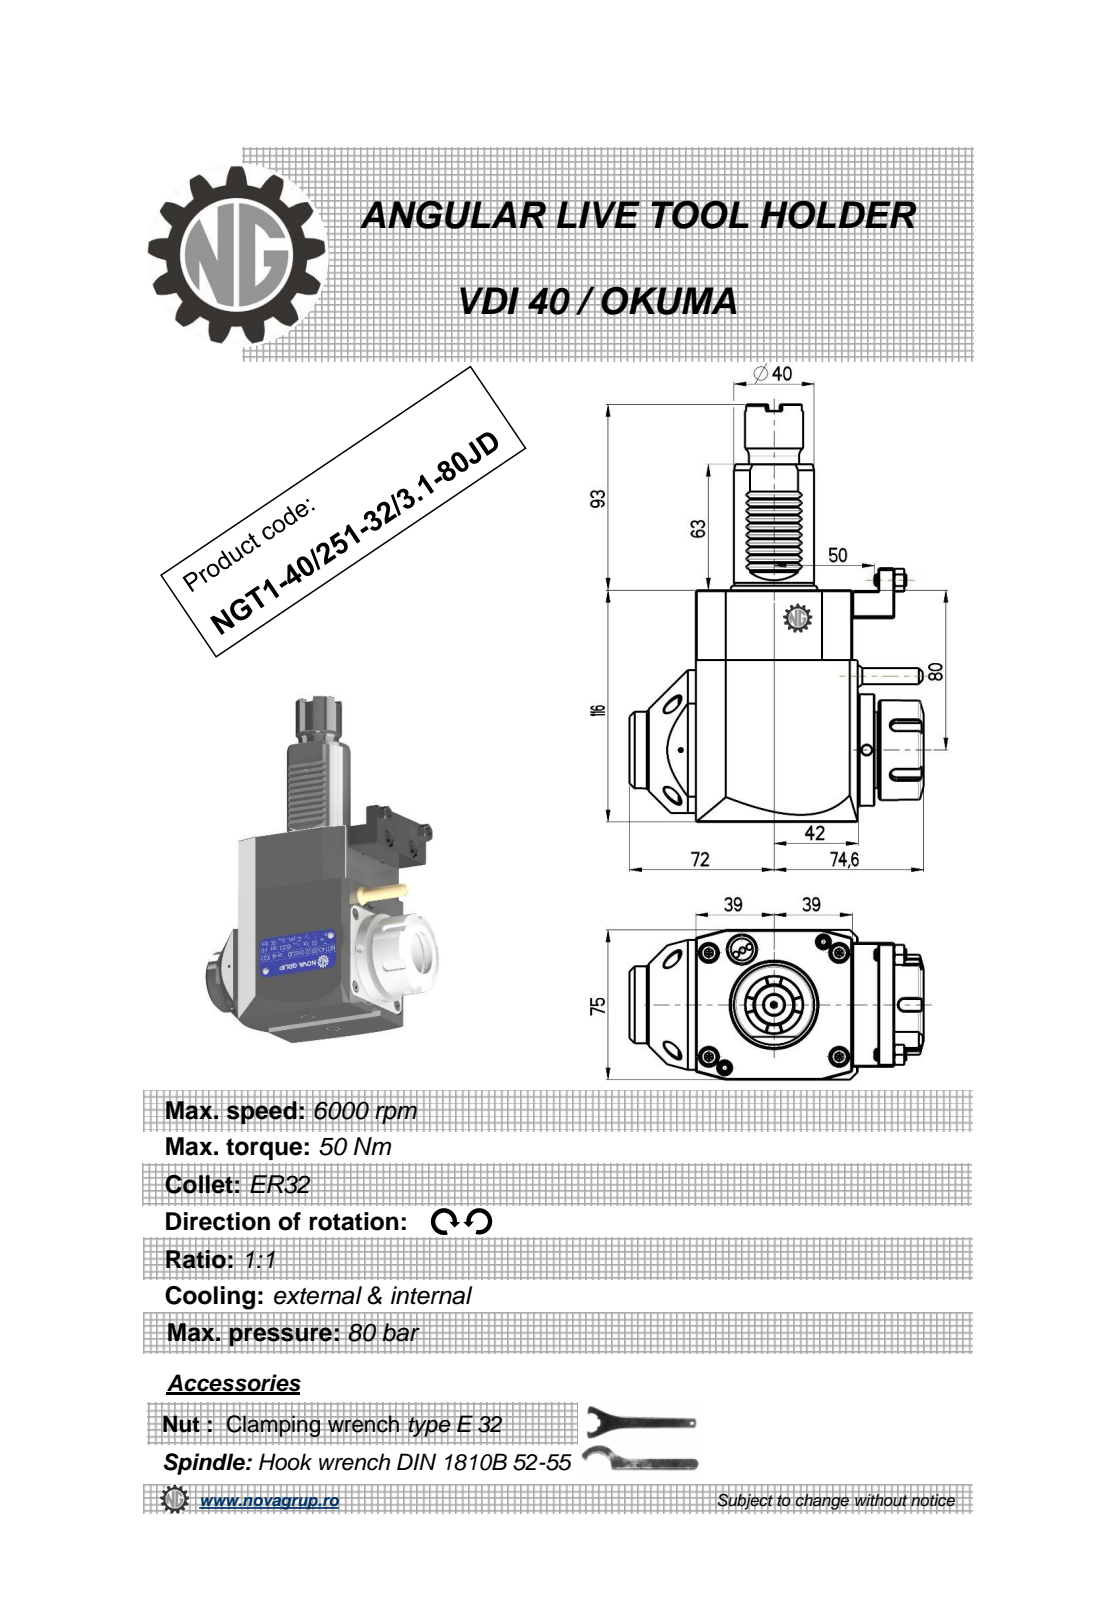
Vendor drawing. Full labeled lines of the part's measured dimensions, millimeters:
Part name (STEP PRODUCT): NGT1_40_251_32_3_1_80JD
STEP written by: PRO/ENGINEER BY PARAMETRIC TECHNOLOGY CORPORATION, 2010280 (CONFIG_CONTROL_DESIGN)
Units: millimetres
Bodies: 1 solid, 456 faces (189 planar, 87 cylindrical, 180 other)
Overall size (bounding box): 209 × 146.6 × 75
Volume: 942 893 mm³ · Surface area: 77 047 mm²
Round holes (diameter × count): ⌀5 ×3, ⌀3 ×1, ⌀27 ×1
Round bosses / shafts (diameter × count): ⌀6 ×2, ⌀56 ×1, ⌀50 ×1, ⌀44 ×1, ⌀40 ×1, ⌀38.5 ×1, ⌀29 ×1, ⌀25 ×1
Partial cylindrical surfaces — rounded edges, fillets, slot ends (radius × count): R0.3 ×10, R0.31 ×10, R0.2 ×6, R3 ×5, R0.5 ×1, R10 ×1, R40 ×1
Main face-to-face distances: 75, 116, 0.5, 81, 10, 21, 11, 18, 8, 80.8
Hole centre spacings: 40.93
